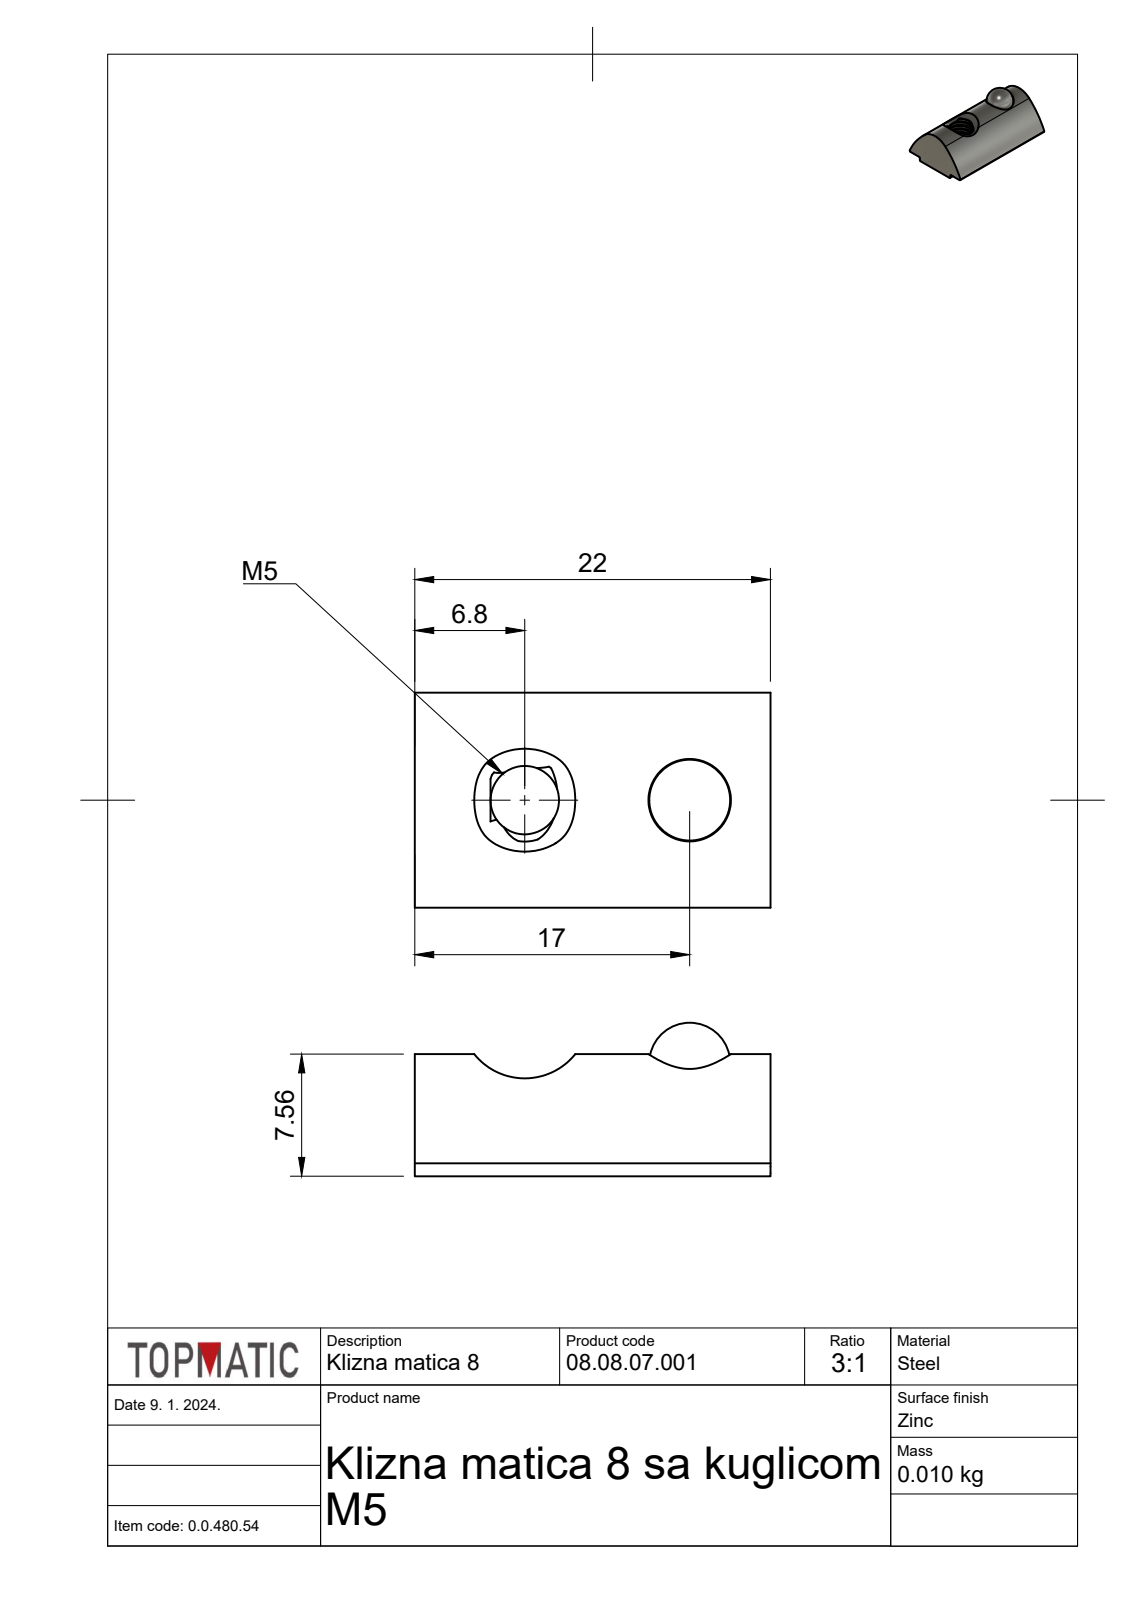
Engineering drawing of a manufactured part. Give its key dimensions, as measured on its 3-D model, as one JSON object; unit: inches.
{"part_name": "Klizna matica 8 M5 v1", "step_written_by": "Autodesk Translation Framework v12.14.0.127 (AUTOMOTIVE_DESIGN)", "units": "inches", "bodies": {"solids": 2, "faces": 46, "planar": 8, "cylindrical": 30, "other": 8}, "overall_size": [0.866, 0.524, 0.374], "volume_in3": 0.08, "surface_area_in2": 1.803, "round_holes": [[0.167, 1], [0.201, 1], [0.202, 1]], "partial_cylinders_radius": [[0.008, 6], [0.157, 2], [0.63, 2]], "face_to_face_distances": [0.031, 0.866, 0.315, 0.231, 0.263], "hole_center_spacings": [0.402]}
